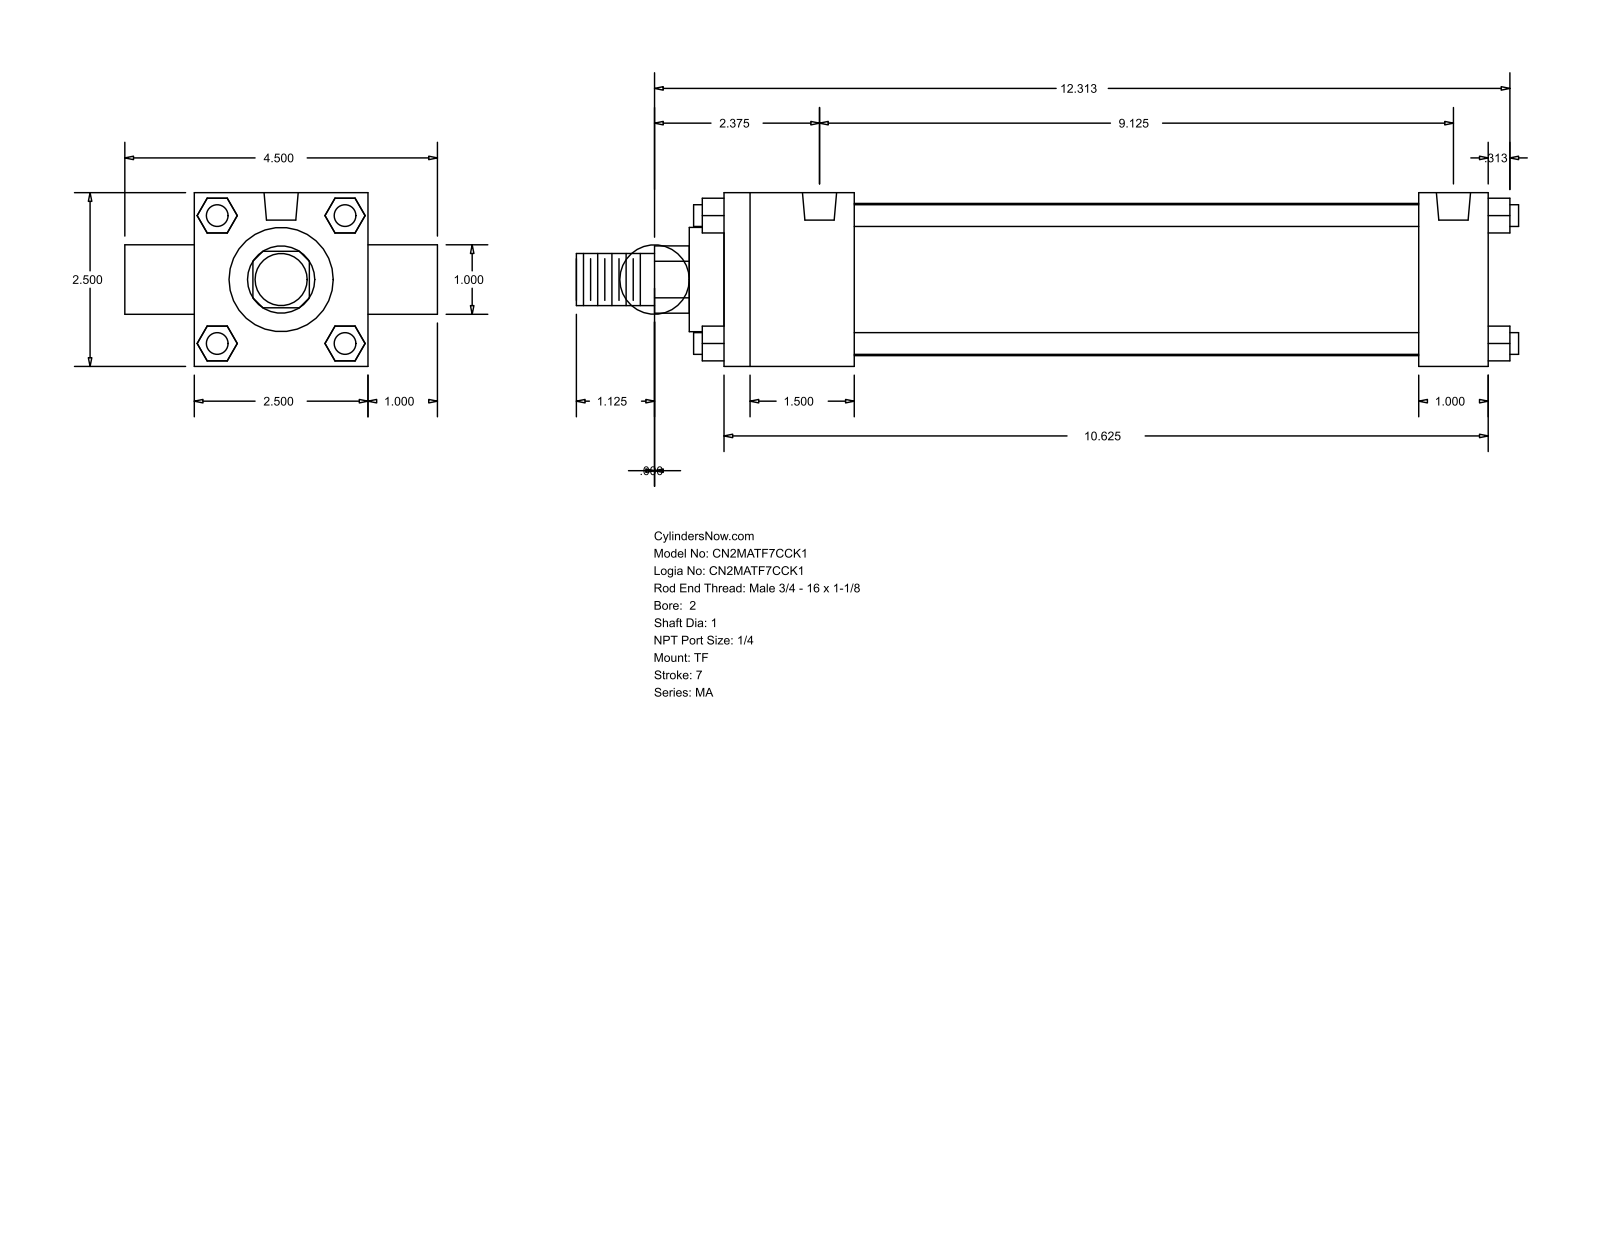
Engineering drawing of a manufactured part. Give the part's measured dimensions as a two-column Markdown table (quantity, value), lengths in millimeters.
| quantity | value |
| --- | --- |
| part name | MA_TF__0200_1 |
| STEP written by | GSSL Pune (CONFIG_CONTROL_DESIGN) |
| units | millimeters |
| bodies | 0 solids, 120 faces (92 planar, 28 cylindrical, 0 other) |
| overall size | 344.49 × 114.3 × 63.5 |
| round holes (diameter × count) | 7.94 × 3, 12.49 × 2 |
| round bosses / shafts (diameter × count) | 7.94 × 4, 25.4 × 2, 55.63 × 1, 38.1 × 1, 19.05 × 1 |
| partial cylindrical surfaces (radius × count) | 12.29 × 1 |
| main face-to-face distances | 63.5, 25.4, 279.4, 12.7, 47.63, 254, 206.37, 231.77, 88.9, 40.47 |
| hole center spacings | 231.77 |
